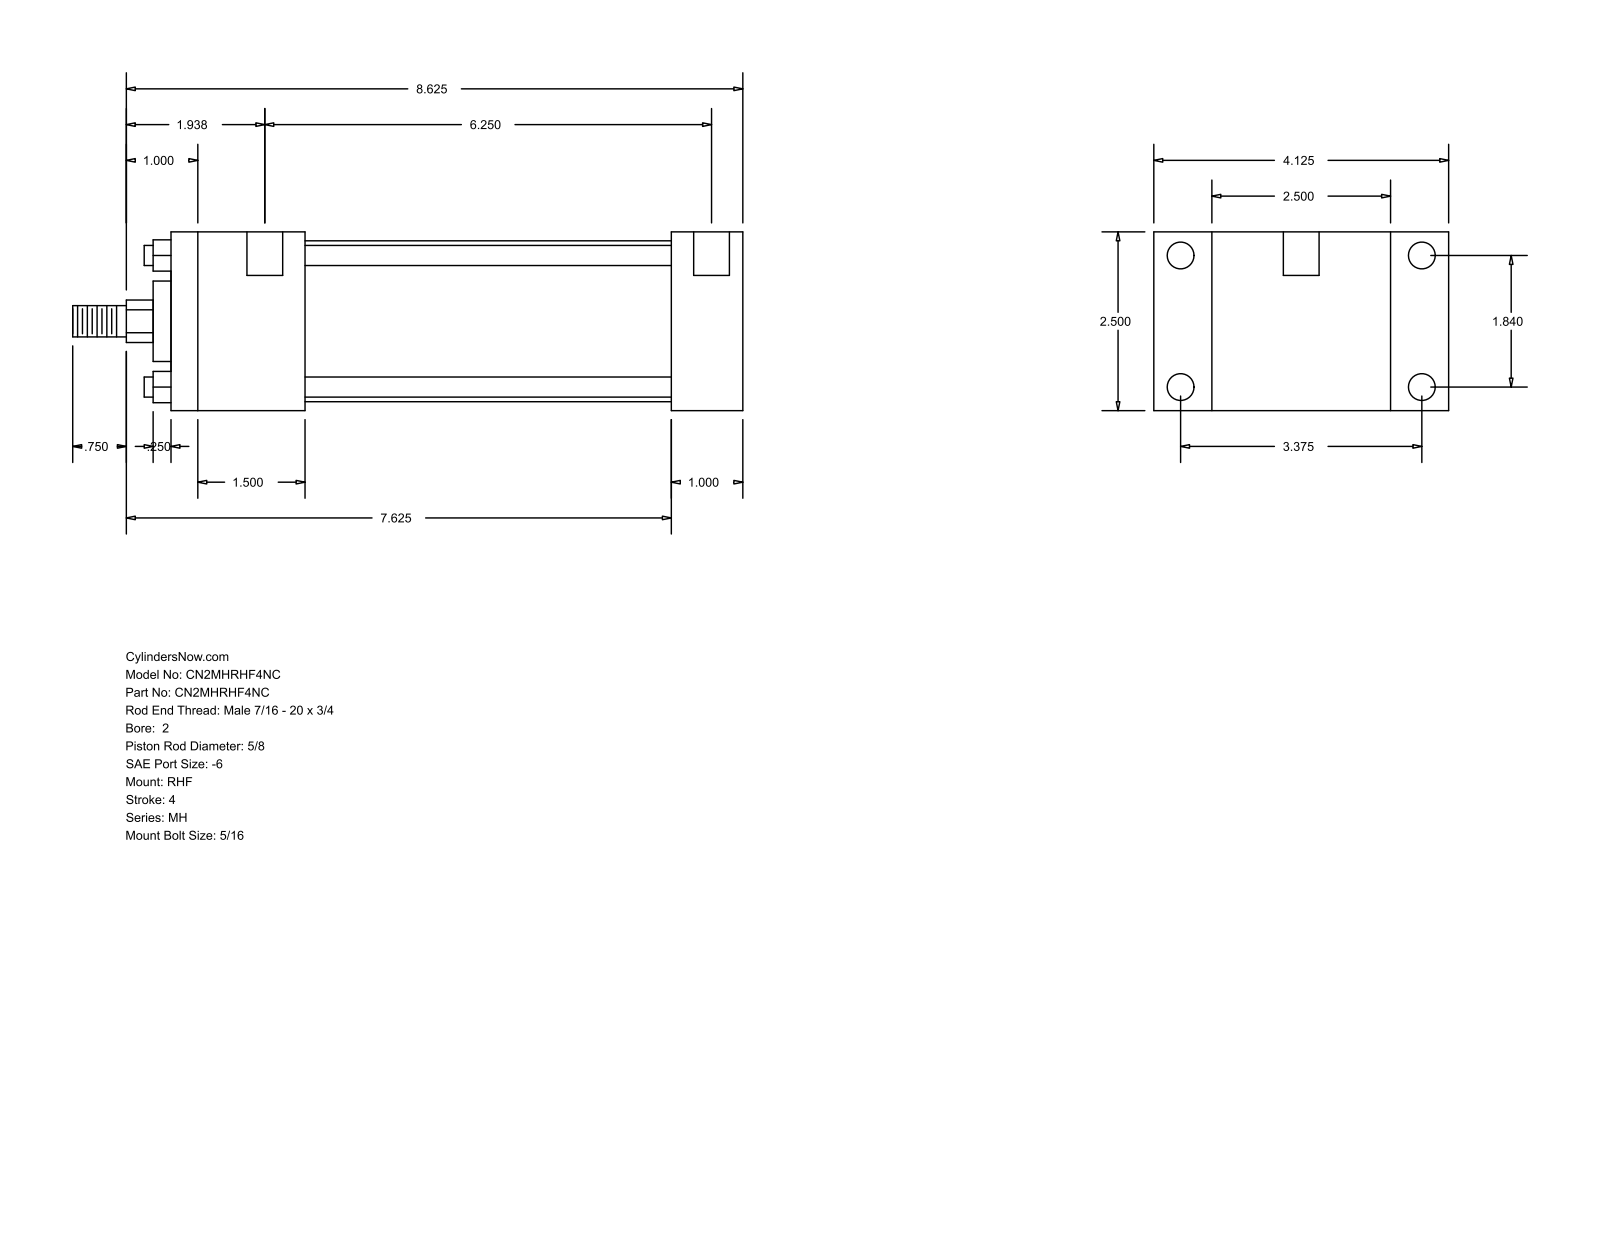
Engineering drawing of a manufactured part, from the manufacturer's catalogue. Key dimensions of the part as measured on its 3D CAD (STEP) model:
Part name (STEP PRODUCT): MH_RHF__0200_0.625
STEP written by: GSSL Pune (CONFIG_CONTROL_DESIGN)
Units: millimetres
Bodies: 0 solids, 88 faces (60 planar, 28 cylindrical, 0 other)
Overall size (bounding box): 238.12 × 104.78 × 63.5
Round holes (diameter × count): ⌀5.56 ×4, ⌀9.53 ×4, ⌀12.7 ×2
Round bosses / shafts (diameter × count): ⌀7.14 ×4, ⌀57.15 ×1, ⌀28.57 ×1, ⌀15.88 ×1, ⌀11.11 ×1
Partial cylindrical surfaces — rounded edges, fillets, slot ends (radius × count): R7.54 ×1
Main face-to-face distances: 63.5, 25.39, 20.64, 84.14, 177.8, 203.19, 104.78, 47.62, 130.18, 155.57
Hole centre spacings: 46.74, 85.72, 97.63, 166.69, 3.18, 4.76, 158.75, 161.93
